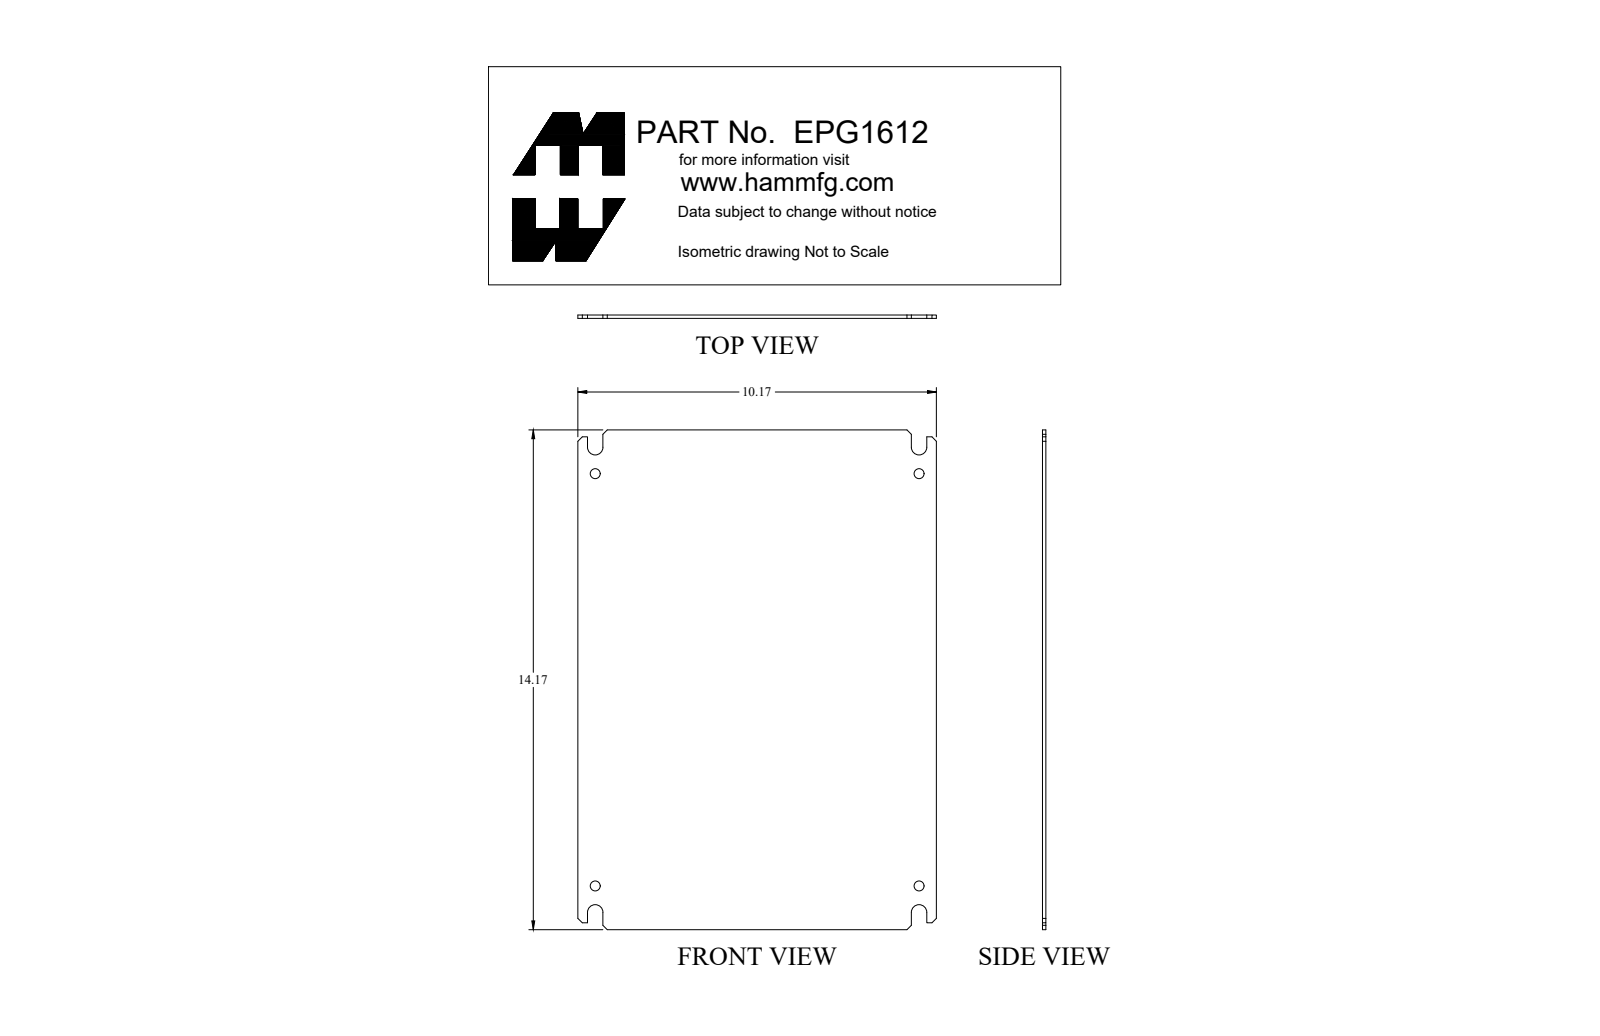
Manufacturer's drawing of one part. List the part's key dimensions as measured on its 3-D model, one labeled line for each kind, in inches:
Part name (STEP PRODUCT): EPG1612
STEP written by: SolidWorks 2018 (AUTOMOTIVE_DESIGN)
Units: inches
Bodies: 1 solid, 40 faces (26 planar, 14 cylindrical, 0 other)
Overall size (bounding box): 14.17 × 10.17 × 0.095
Volume: 13.53 in³ · Surface area: 290.1 in²
Round holes (diameter × count): ⌀0.281 ×4
Partial cylindrical surfaces — rounded edges, fillets, slot ends (radius × count): R0.219 ×4
Main face-to-face distances: 0.095, 10.17, 14.17, 0.709, 9.461, 0.272, 9.898, 0.437, 9.188, 8.751
Hole centre spacings: 9.188, 11.688, 14.867
